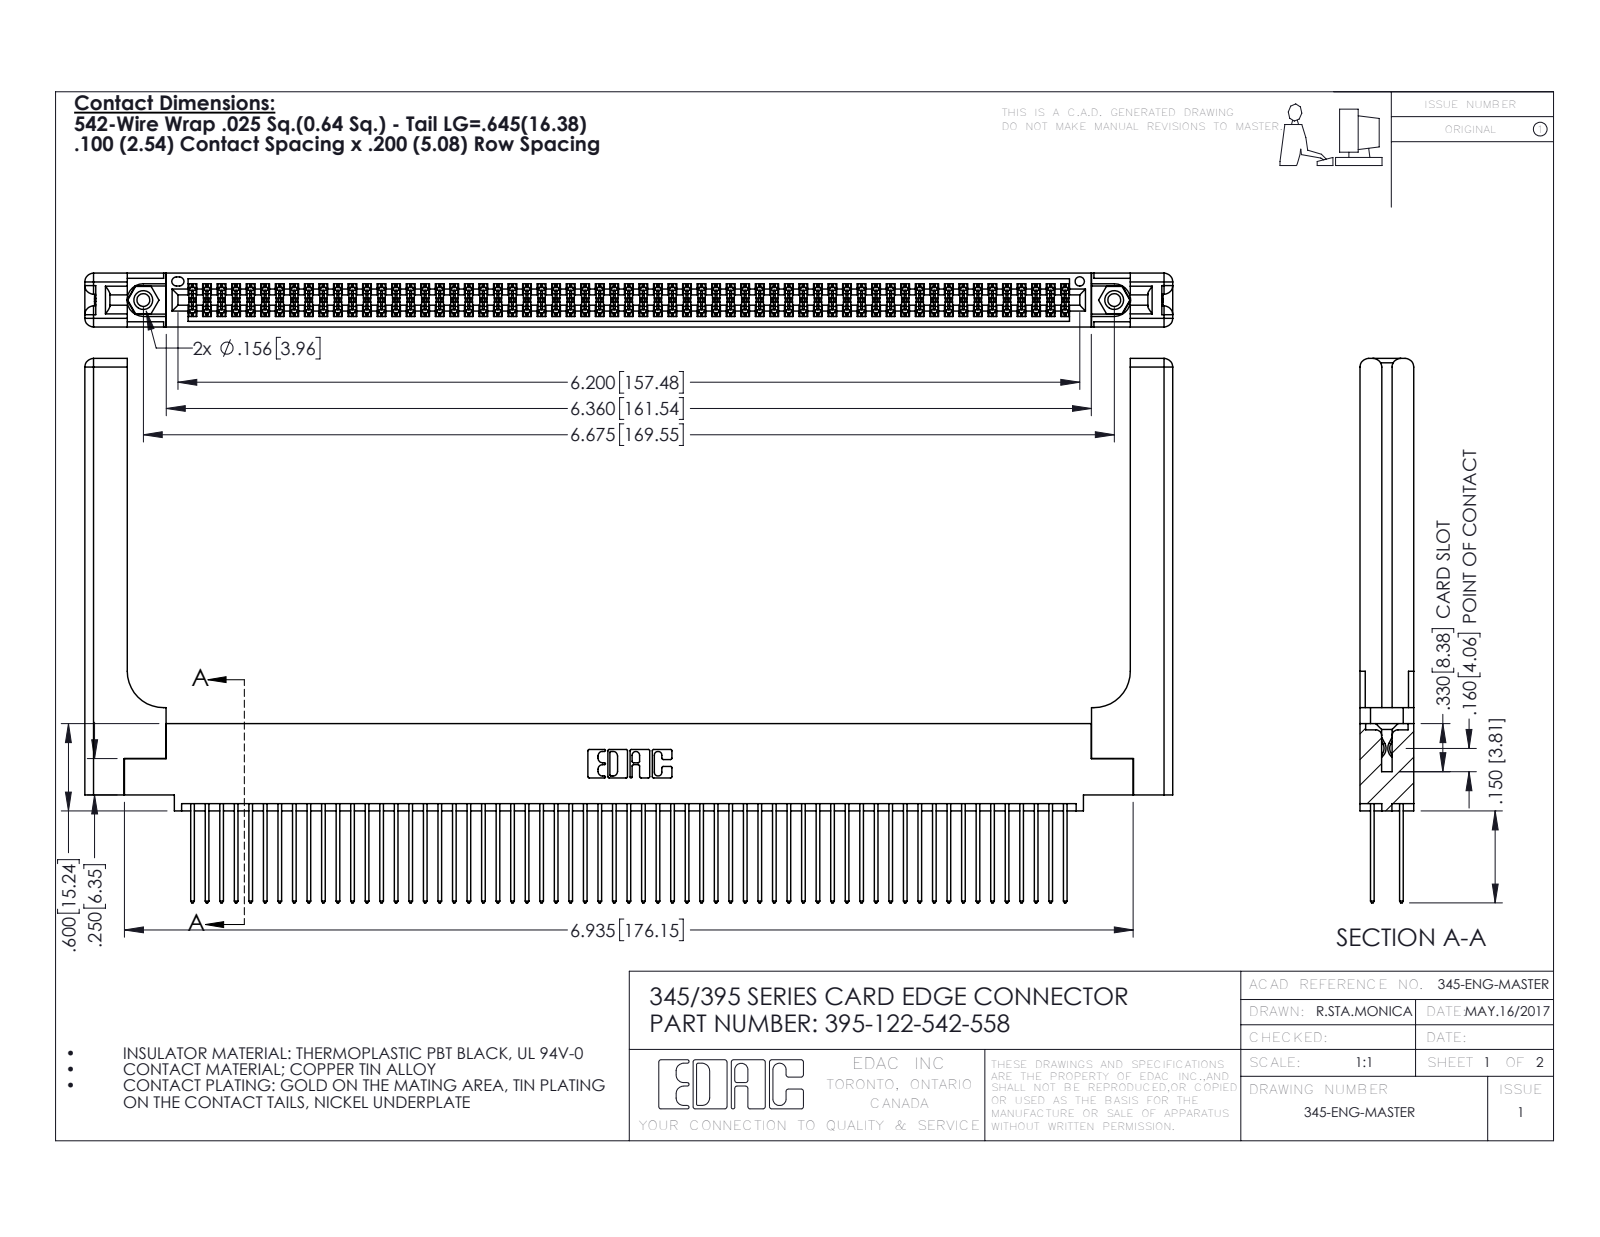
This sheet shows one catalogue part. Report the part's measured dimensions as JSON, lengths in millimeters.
{"part_name": "345-292-001_345-293-142; 345-250-001_345-250-001-102; 395-122-542-558; 345 Part_0.110 Offset - 0.156 Dia-TH (+1 more)", "step_written_by": "SolidWorks 2016 (CONFIG_CONTROL_DESIGN)", "units": "millimeters", "bodies": {"solids": 127, "faces": 6486, "planar": 4258, "cylindrical": 2168, "other": 60}, "overall_size": [190, 95, 9.4], "volume_mm3": 27600, "surface_area_mm2": 36450, "round_holes": [[2.3, 2], [3.2, 2], [4, 2], [1.6, 1]], "round_bosses_or_shafts": [[3.9, 2]], "partial_cylinders_radius": [[0.2, 183], [0.3, 122], [0.3, 22], [1.5, 16], [0.2, 6], [0.8, 6], [0.7, 3], [0.4, 2]], "face_to_face_distances": [1.8, 7.6, 9.4, 2.5, 6.9, 0.6, 5.1, 5.7, 4.4, 3.8], "hole_center_spacings": [6.9, 163.6, 169.5]}
